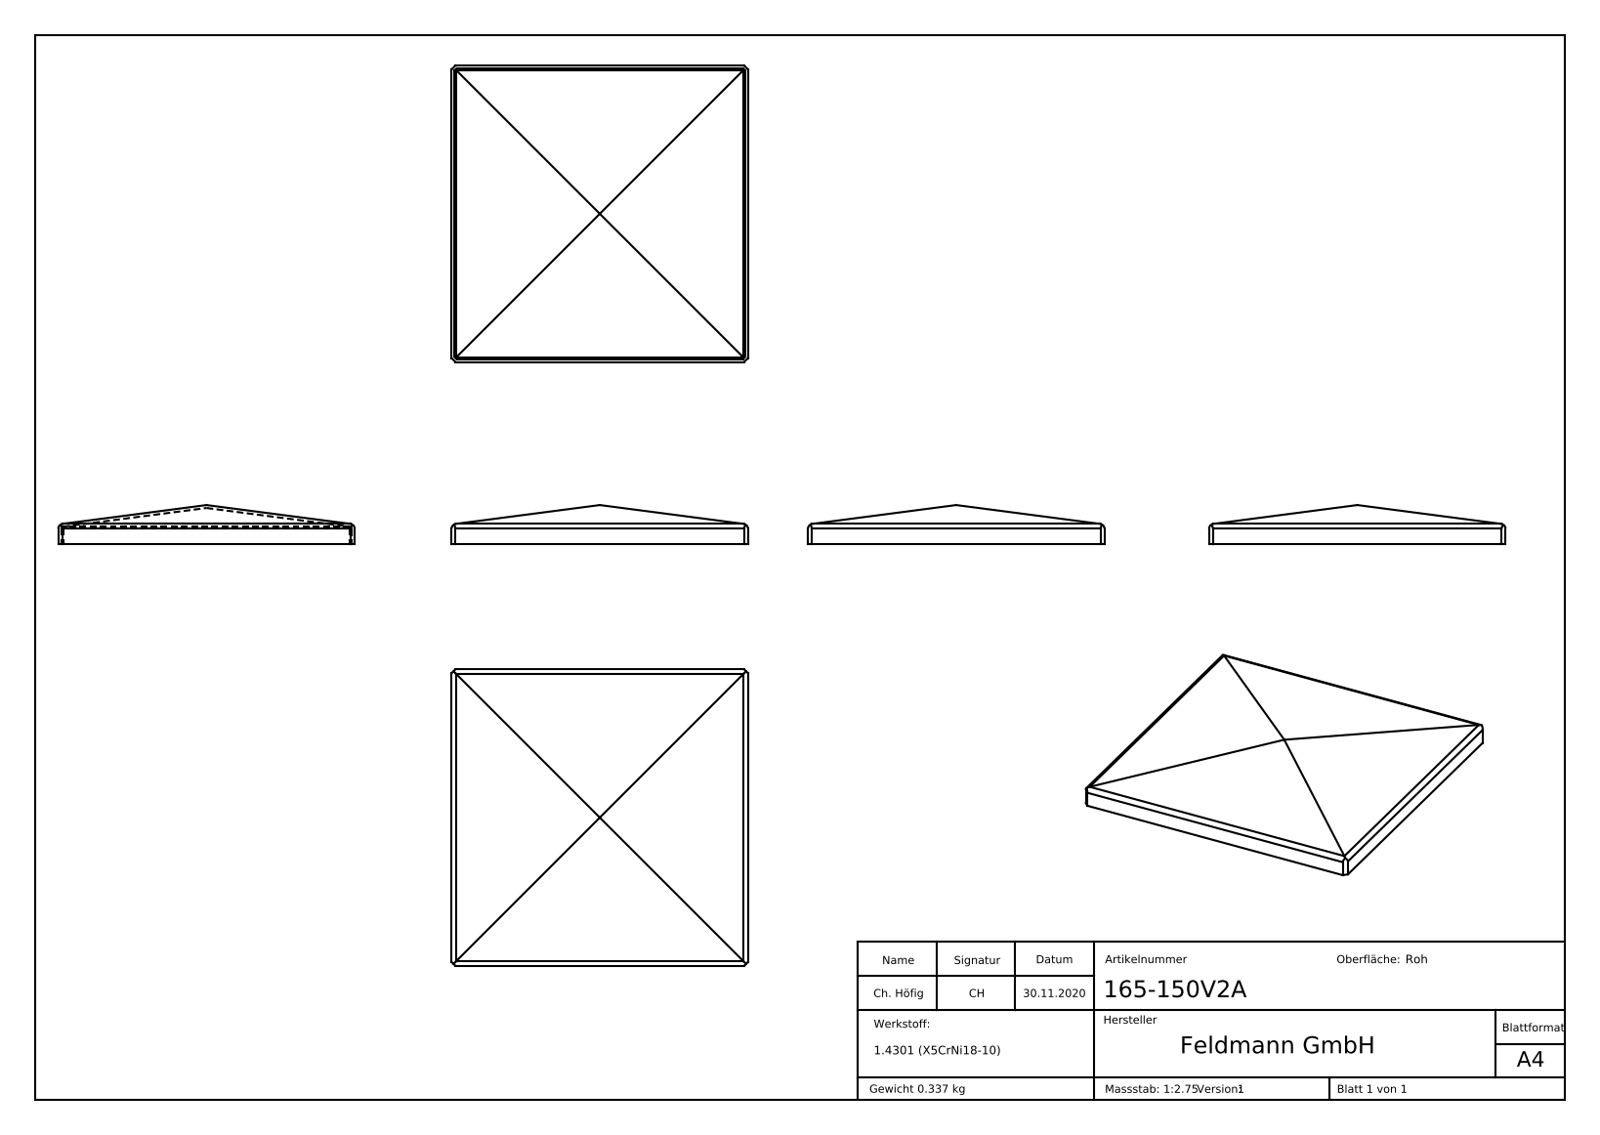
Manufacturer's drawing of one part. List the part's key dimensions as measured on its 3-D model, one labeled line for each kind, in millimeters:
Part name (STEP PRODUCT): 165-150V2A
STEP written by: SolidWorks 2018 (CONFIG_CONTROL_DESIGN)
Units: millimetres
Bodies: 1 solid, 258 faces (158 planar, 12 cylindrical, 88 other)
Overall size (bounding box): 153 × 153 × 20
Volume: 42 661 mm³ · Surface area: 57 797 mm²
Partial cylindrical surfaces — rounded edges, fillets, slot ends (radius × count): R1 ×4, R2.5 ×4, R0.1 ×2
Main face-to-face distances: 1.5, 151.5, 153, 150, 212.02, 213.52, 210.52, 1.4, 150.1, 151.6
